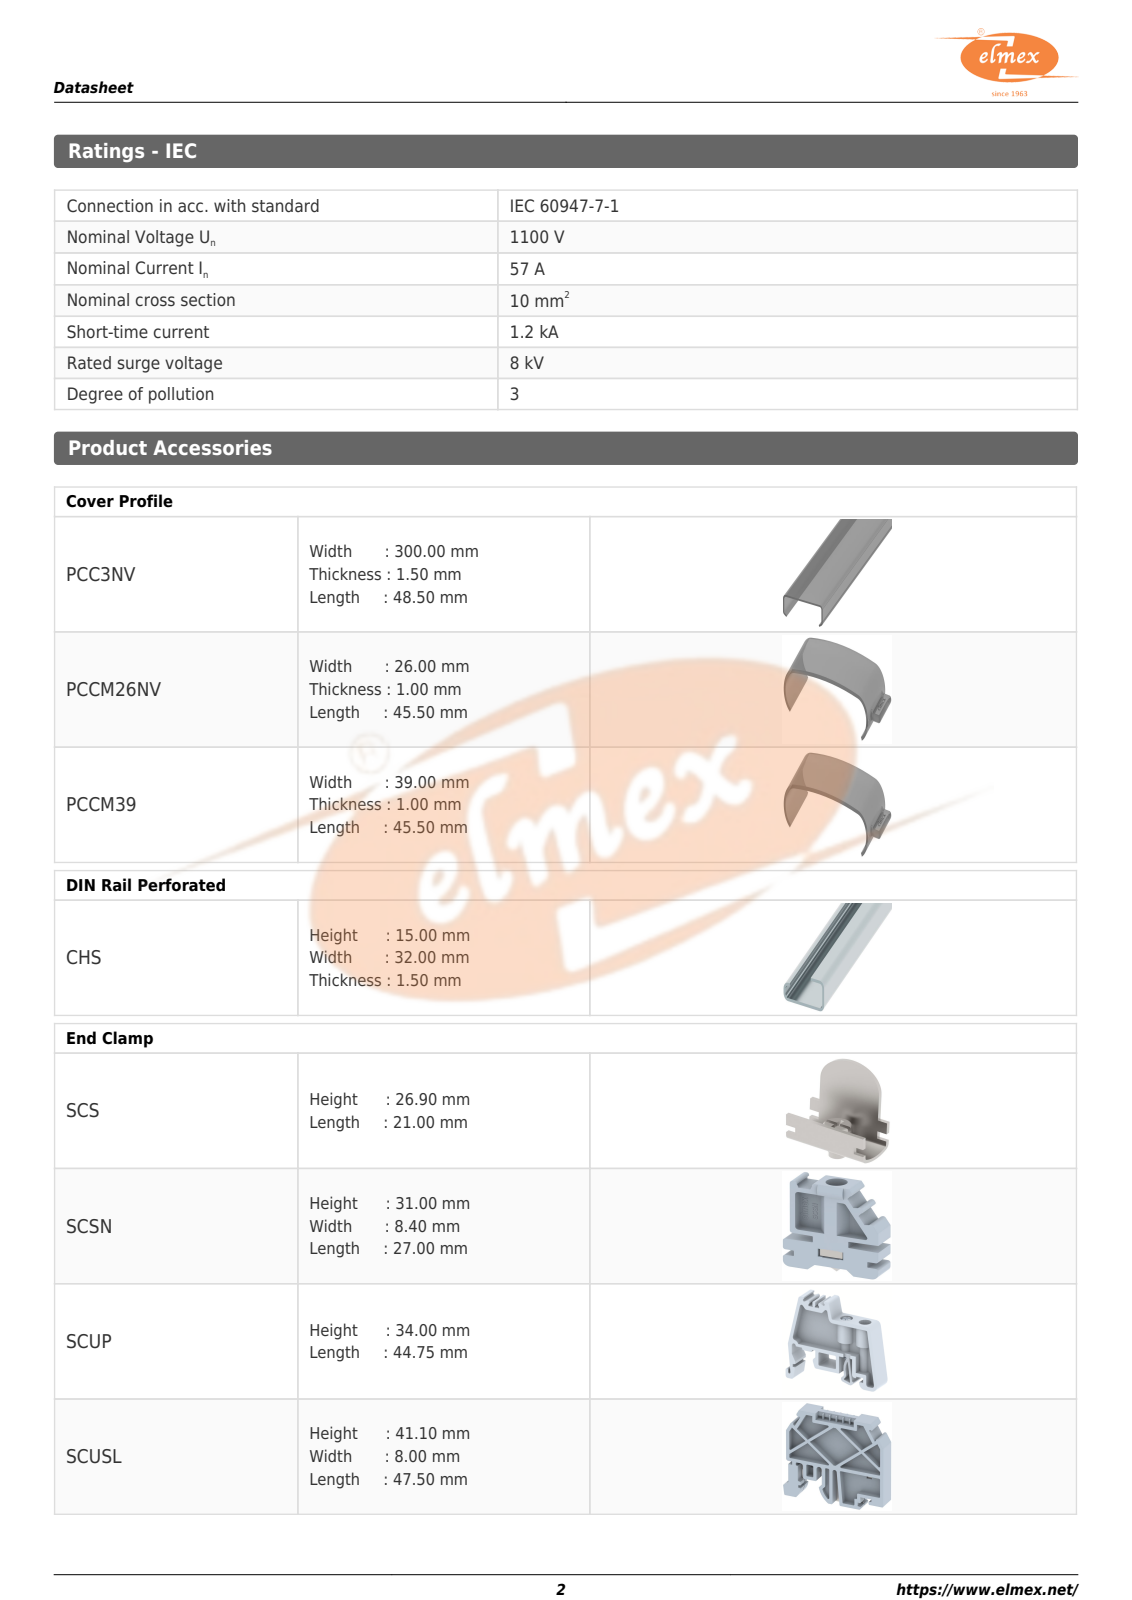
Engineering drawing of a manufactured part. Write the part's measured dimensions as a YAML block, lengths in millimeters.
step_written_by: "ST-DEVELOPER v16 (AUTOMOTIVE_DESIGN)"
units: millimeters
bodies: {solids: 1, faces: 42, planar: 32, cylindrical: 10, other: 0}
overall_size: [50, 45, 13]
volume: 21722
surface_area: 5950
partial_cylinders:
  - {radius: 2, count: 5}
  - {radius: 1.5, count: 2}
  - {radius: 4, count: 2}
  - {radius: 1.65, count: 1}
face_to_face_distances: [13, 45, 50, 41.7, 3.3, 30, 20, 18, 23.7, 27]
